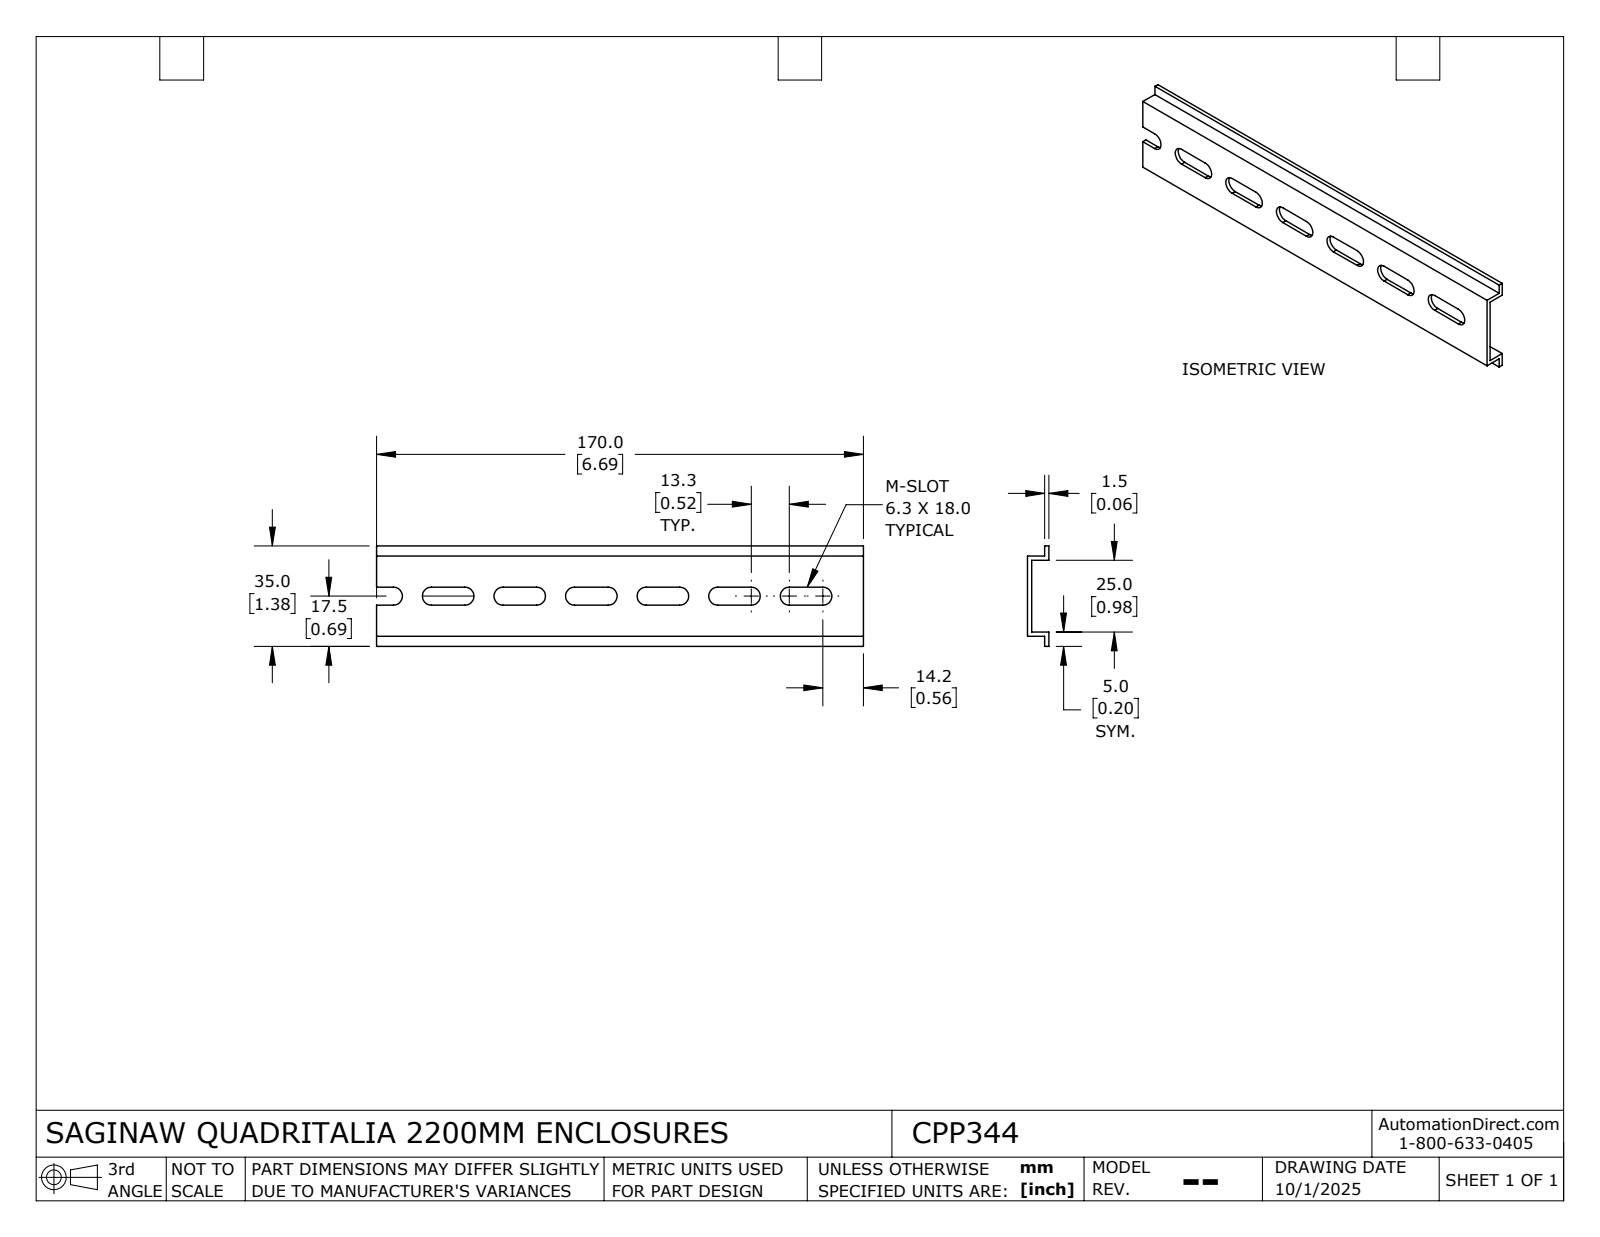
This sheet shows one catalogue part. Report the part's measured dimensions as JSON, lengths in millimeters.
{"part_name": "CPP344_Default", "step_written_by": "SolidWorks 2024 (CONFIG_CONTROL_DESIGN)", "units": "millimeters", "bodies": {"solids": 1, "faces": 42, "planar": 29, "cylindrical": 13, "other": 0}, "overall_size": [170, 35, 7.5], "volume_mm3": 10962, "surface_area_mm2": 15679, "partial_cylinders_radius": [[3.15, 13]], "face_to_face_distances": [1.5, 6, 26.5, 7.5, 4.5, 28, 25, 3.5, 5, 30]}
